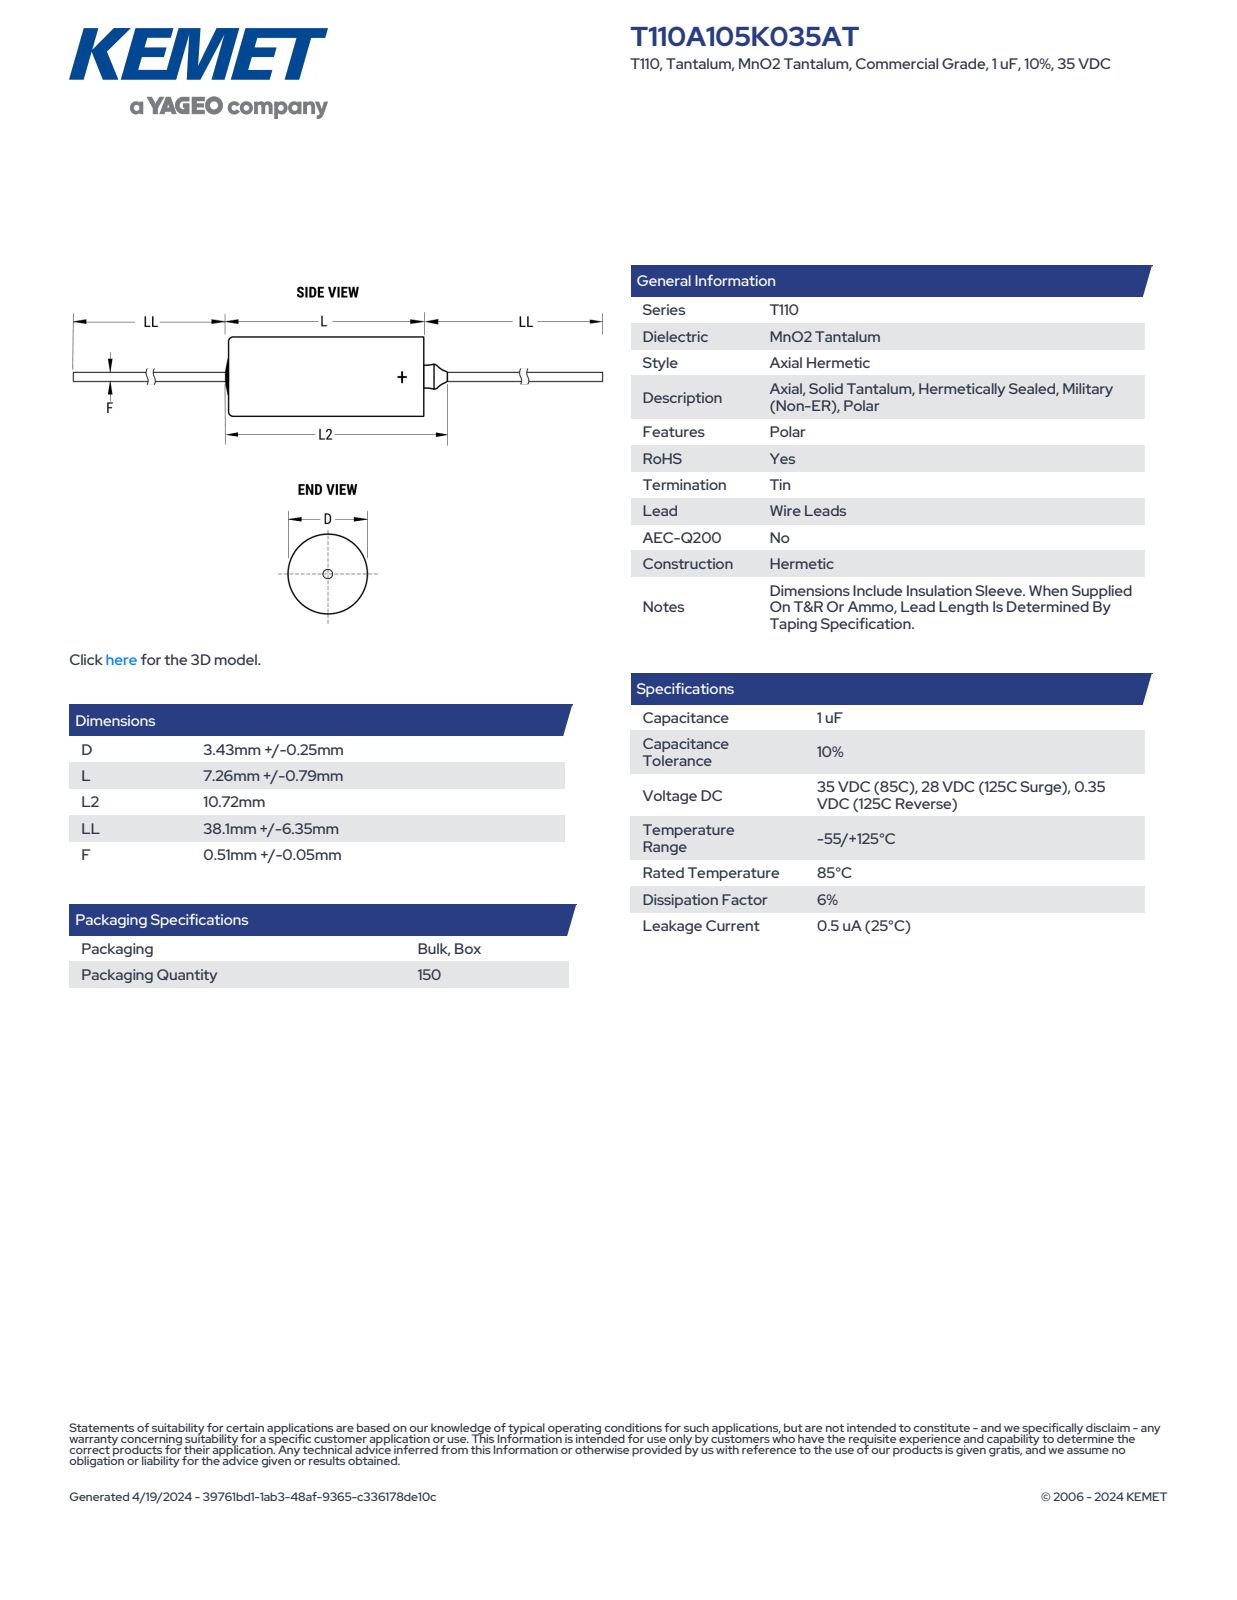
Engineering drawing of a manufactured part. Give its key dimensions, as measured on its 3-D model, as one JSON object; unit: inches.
{"part_name": "CTAM_A_D3.68L8.05L210.72LL44.45F0.56", "step_written_by": "SolidWorks 2014 (AUTOMOTIVE_DESIGN)", "units": "inches", "bodies": {"solids": 1, "faces": 99, "planar": 30, "cylindrical": 30, "other": 39}, "overall_size": [3.817, 0.145, 0.145], "volume_in3": 0.006, "surface_area_in2": 0.468, "round_holes": [[0.129, 1]], "round_bosses_or_shafts": [[0.145, 1], [0.052, 1], [0.051, 1], [0.022, 1]], "partial_cylinders_radius": [[0.072, 1]], "face_to_face_distances": [0.231, 0.31, 0.079, 1.75, 2.067, 1.757, 1.988, 3.817, 2.06, 1.829]}
